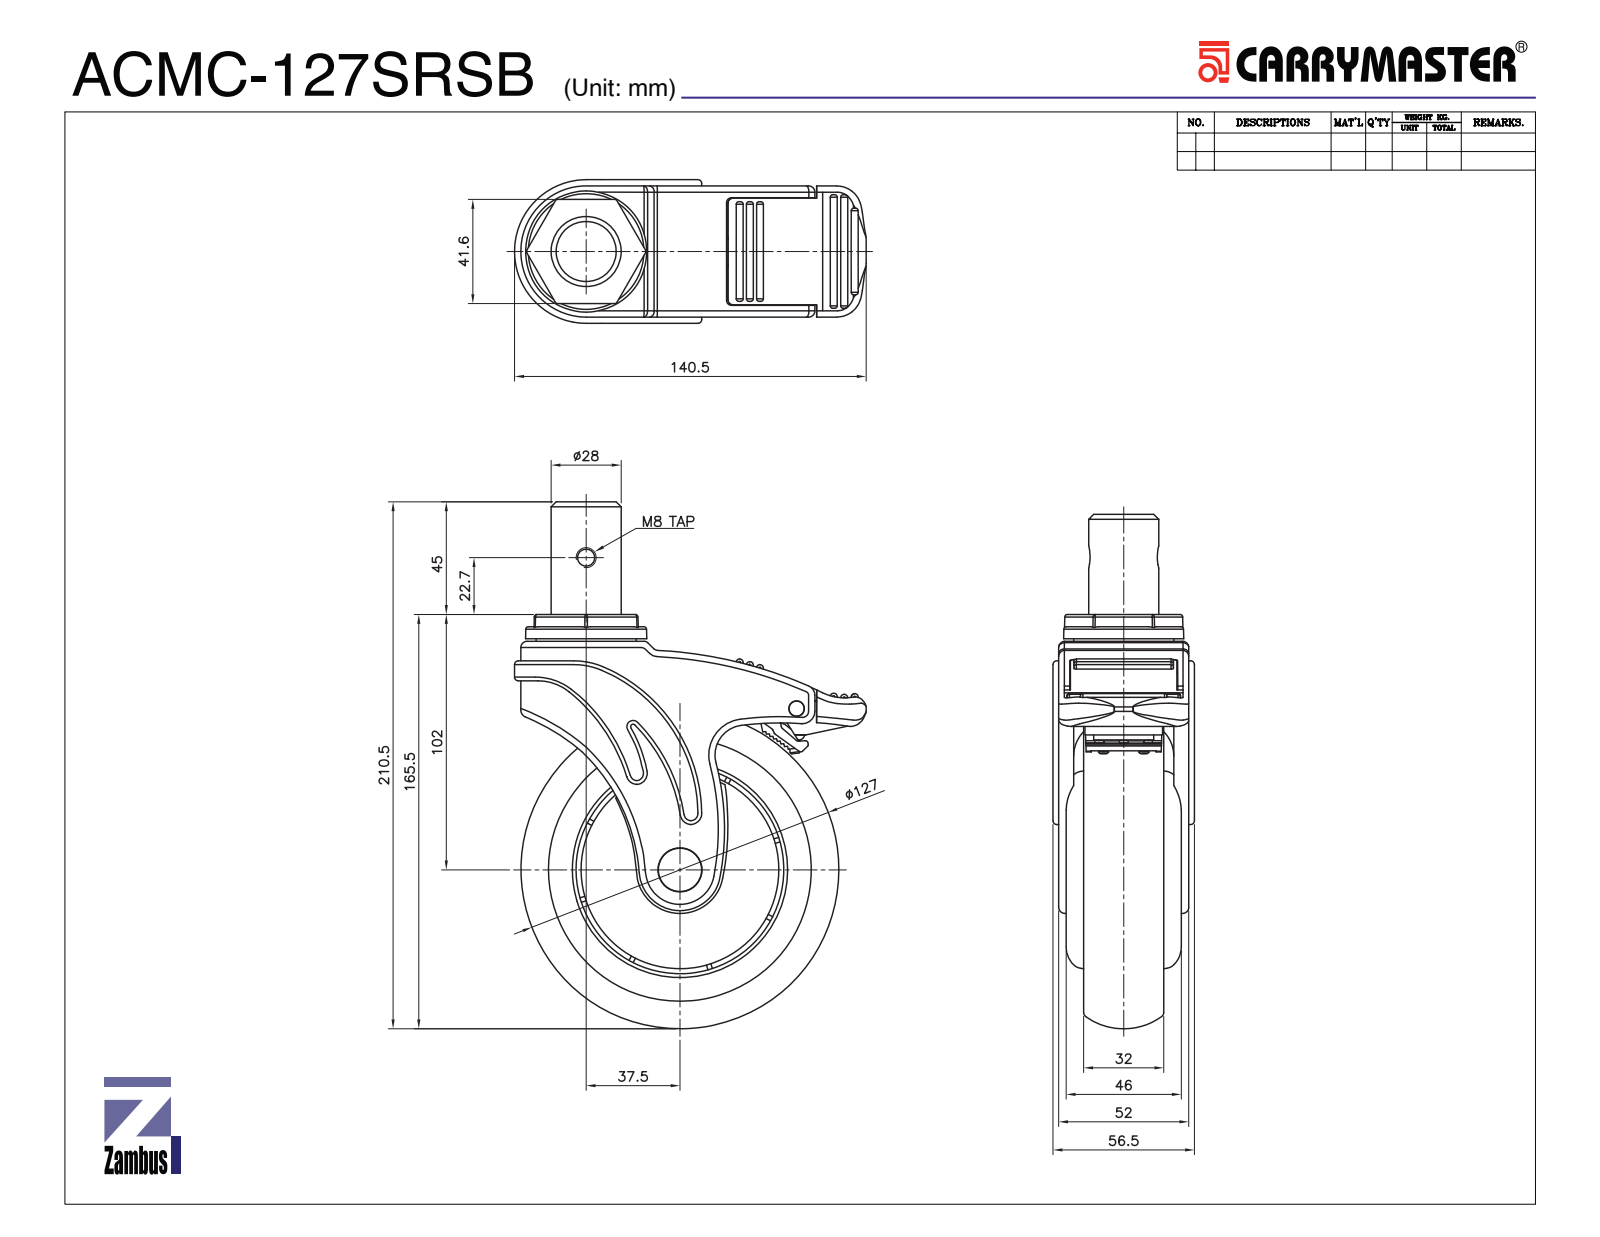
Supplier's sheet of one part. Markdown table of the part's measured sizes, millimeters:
| quantity | value |
| --- | --- |
| part name | ACMC-127 WHEEL; ACMC-127 BRAKE; ACMC-127SRSB; ACMC-127 TOP PLATE COVER (+2 more) |
| STEP written by | SolidWorks 2019 (CONFIG_CONTROL_DESIGN) |
| units | millimeters |
| bodies | 6 solids, 659 faces (215 planar, 272 cylindrical, 172 other) |
| overall size | 210.5 × 141.04 × 57.1 |
| volume | 625 160 mm³ |
| surface area | 106 065 mm² |
| round holes (diameter × count) | 6.8 × 1, 8 × 1, 17.3 × 1, 37 × 1, 83 × 1, 105.01 × 1 |
| round bosses / shafts (diameter × count) | 4 × 2, 105 × 1, 79 × 1, 78.59 × 1, 40 × 1, 28 × 1, 22 × 1, 17 × 1 |
| partial cylindrical surfaces (radius × count) | 0.5 × 27, 1 × 16, 2 × 8, 1.4 × 6, 2.5 × 6, 4.5 × 4, 1.5 × 2, 10 × 2 |
| main face-to-face distances | 4.25, 36.25, 6, 10.25, 42.25, 46.5, 32, 40.5, 4, 6.25 |
| hole center spacings | 130.22 |
